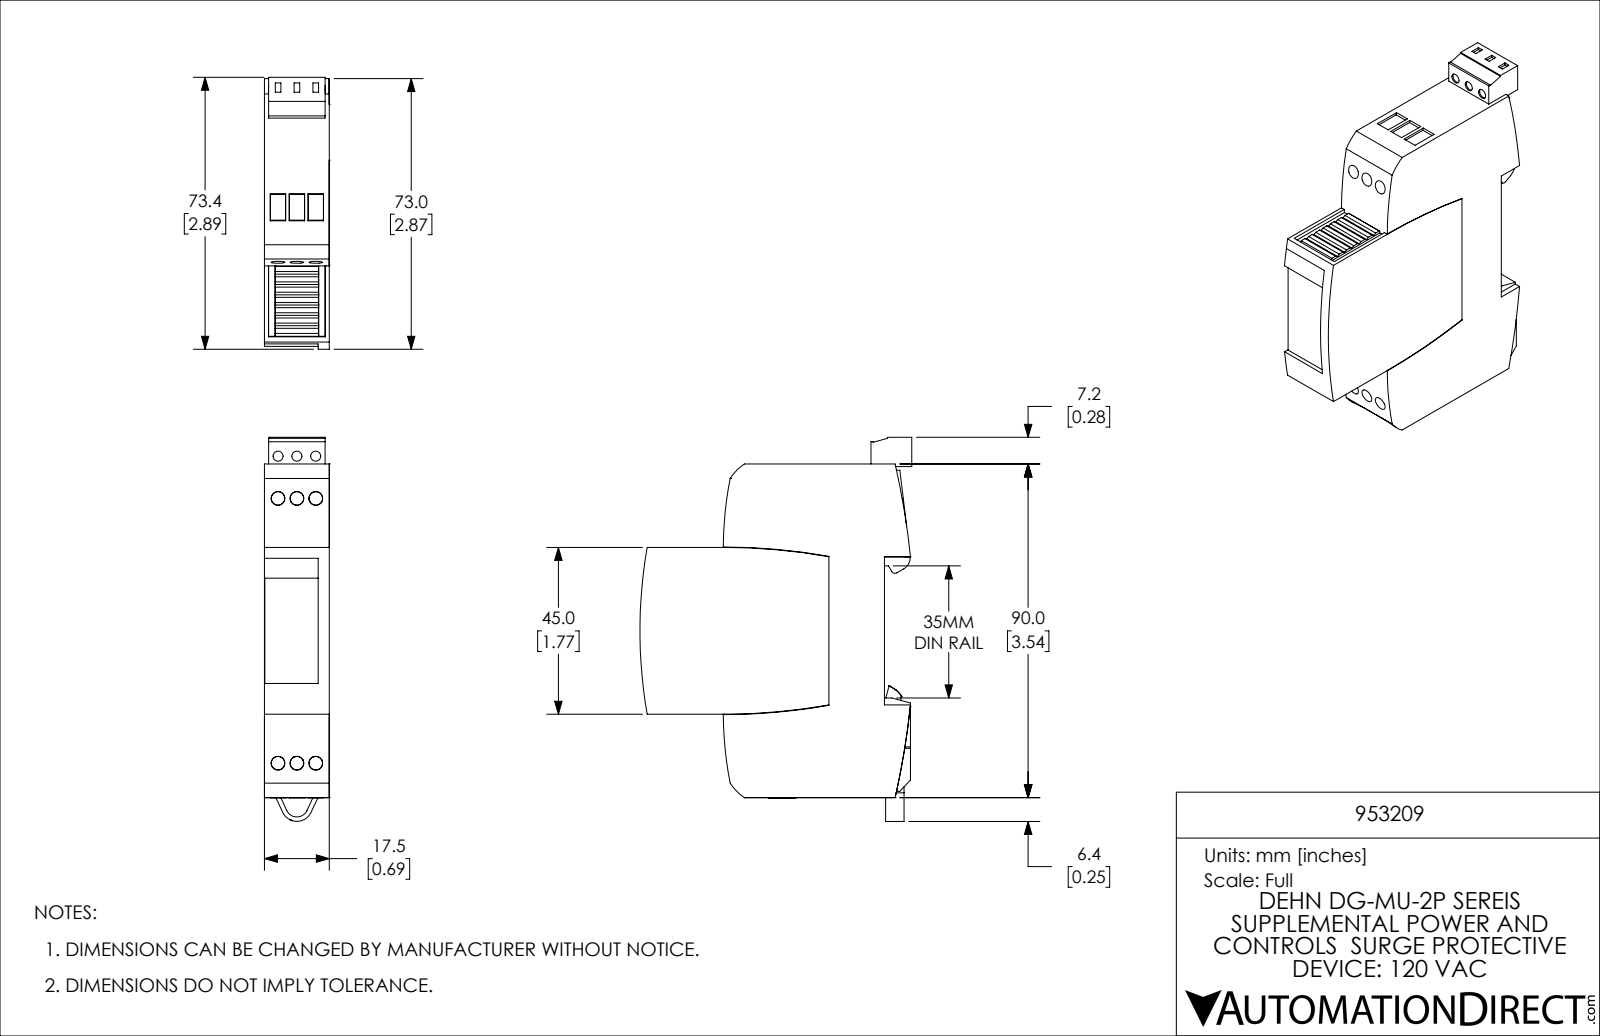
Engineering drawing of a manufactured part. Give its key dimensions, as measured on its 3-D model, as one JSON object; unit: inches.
{"part_name": "953209", "step_written_by": "SolidWorks 2019 (CONFIG_CONTROL_DESIGN)", "units": "inches", "bodies": {"solids": 1, "faces": 255, "planar": 198, "cylindrical": 38, "other": 19}, "overall_size": [4.079, 2.888, 0.689], "volume_in3": 5.435, "surface_area_in2": 27.21, "round_holes": [[0.106, 3]], "partial_cylinders_radius": [[6.448, 2], [6.449, 2], [0.039, 1], [0.098, 1], [0.118, 1], [0.138, 1], [3.937, 1], [3.94, 1]], "face_to_face_distances": [0.689, 0.685, 3.543, 0.016, 0.673, 2.518, 0.276, 2.794, 0.898, 2.646], "hole_center_spacings": [0.2, 0.4]}
